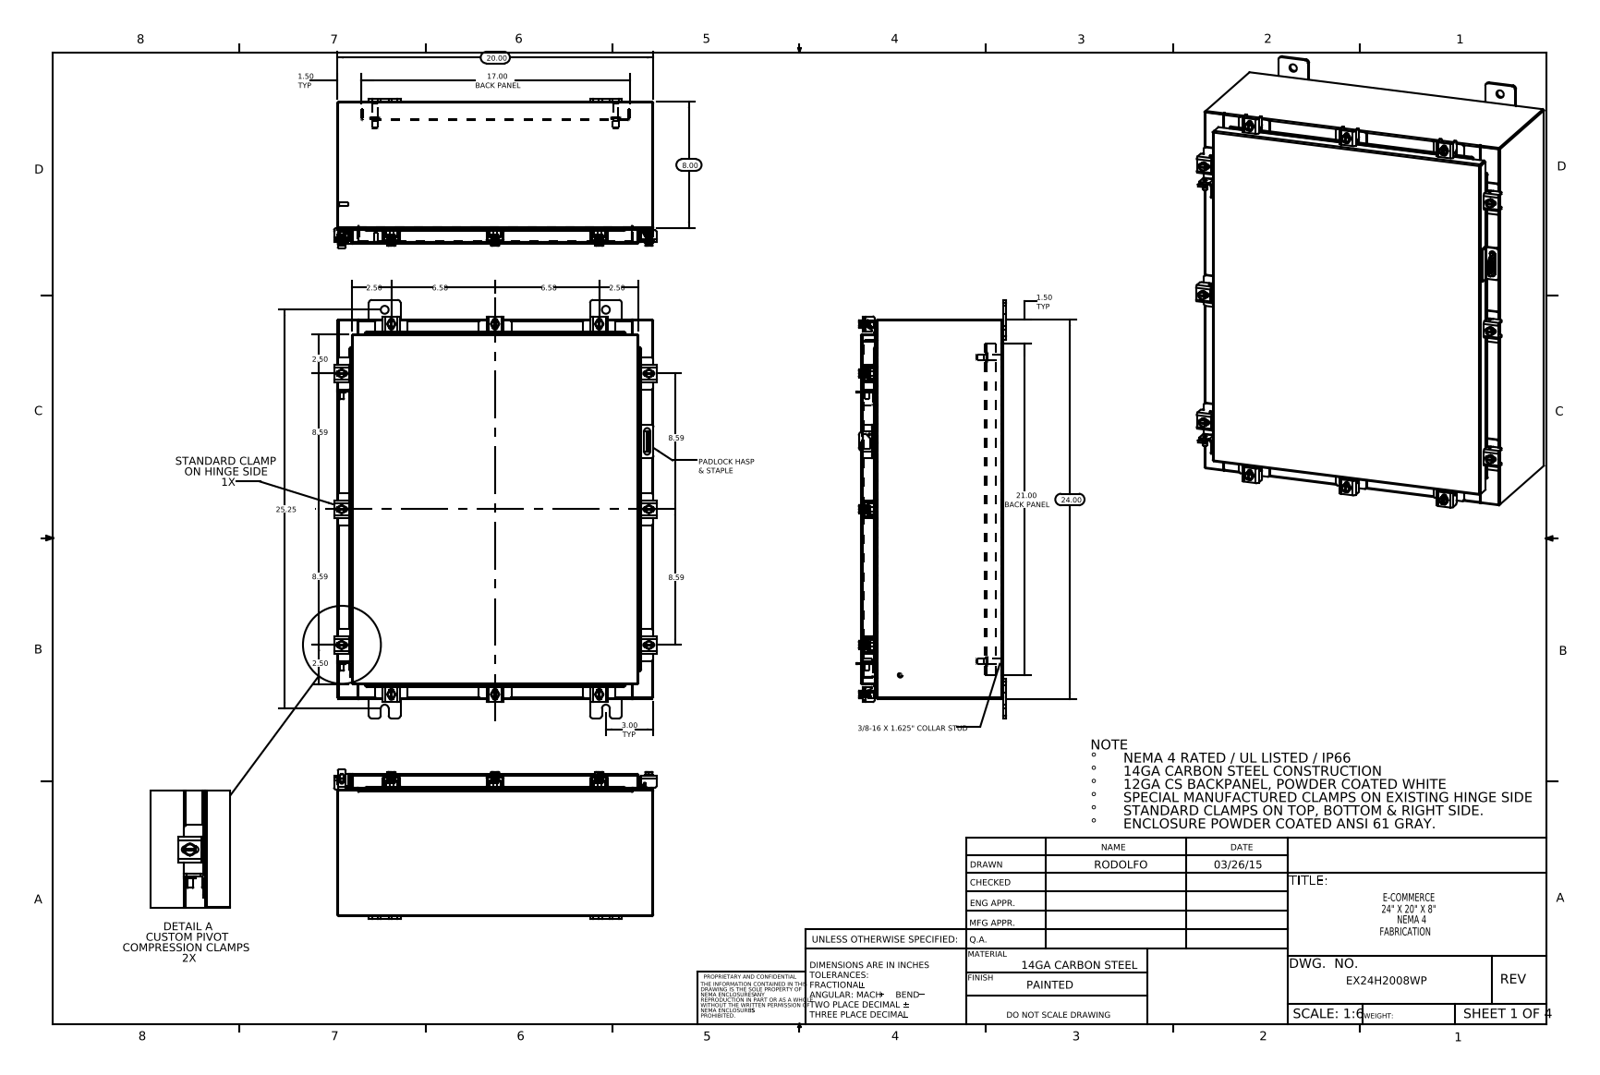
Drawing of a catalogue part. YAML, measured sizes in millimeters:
part_name: "EX24H2008WP Special Clamp; ATEX CLAMP HINGE BRAKET; EX24H2008WP Padlock Hasp; EX24H2008WP Cover (+8 more)"
step_written_by: "SolidWorks 2014 (CONFIG_CONTROL_DESIGN)"
units: millimeters
bodies: {solids: 81, faces: 2018, planar: 1075, cylindrical: 783, other: 160}
overall_size: [673.1, 518.7, 240.1]
volume: 3068000
surface_area: 3023000
round_holes:
  - {diameter: 5.4, count: 12}
  - {diameter: 6.6, count: 12}
  - {diameter: 12.7, count: 8}
  - {diameter: 3.2, count: 1}
  - {diameter: 6.4, count: 1}
round_bosses_or_shafts:
  - {diameter: 12.7, count: 12}
  - {diameter: 6.4, count: 12}
  - {diameter: 10.1, count: 10}
  - {diameter: 15.9, count: 4}
  - {diameter: 9.5, count: 4}
  - {diameter: 8.4, count: 4}
  - {diameter: 8, count: 2}
  - {diameter: 6, count: 2}
partial_cylinders:
  - {radius: 1.5, count: 54}
  - {radius: 0.3, count: 24}
  - {radius: 3.6, count: 24}
  - {radius: 4.8, count: 24}
  - {radius: 2.2, count: 22}
  - {radius: 3, count: 22}
  - {radius: 2.3, count: 18}
  - {radius: 1.3, count: 17}
face_to_face_distances: [1.9, 226.1, 228, 224.2, 2.6, 506.1, 25.4, 27.3, 198.8, 200.7]
hole_center_spacings: [59.6, 112.8, 218.3, 308.4, 421.7, 465.8, 510.1, 522.3]
